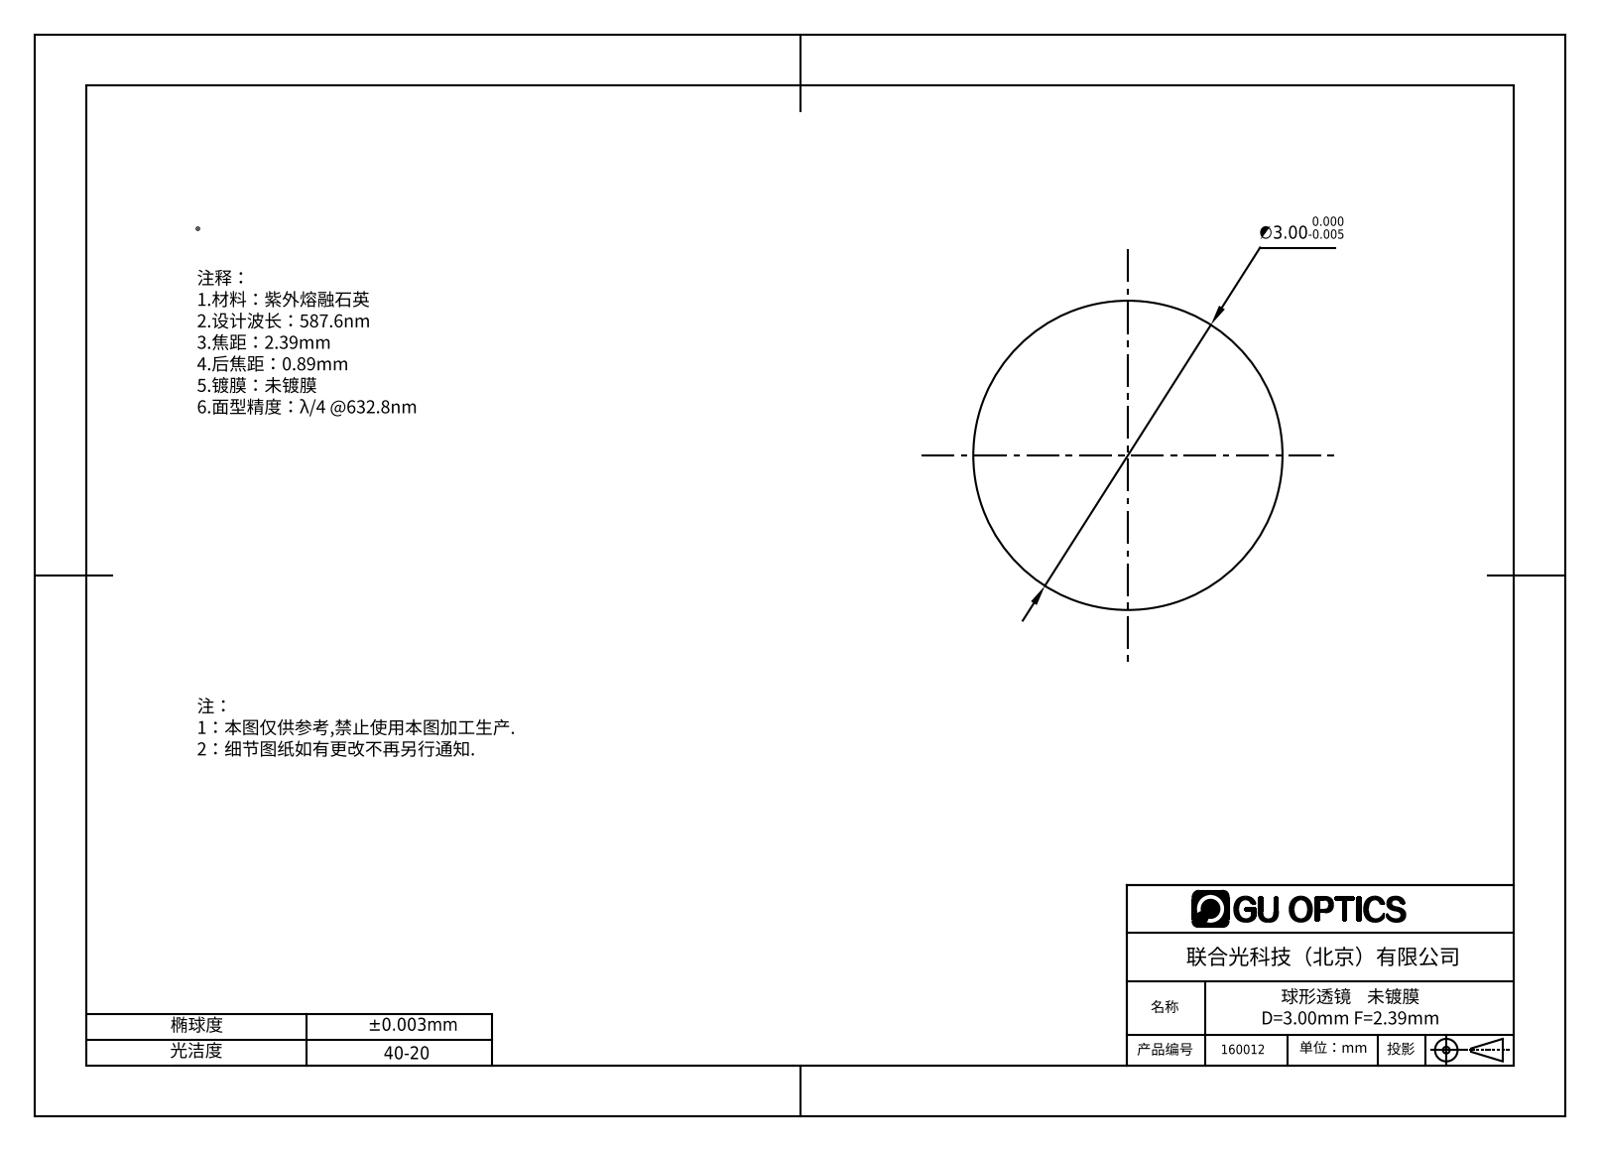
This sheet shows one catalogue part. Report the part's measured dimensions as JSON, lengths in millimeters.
{"part_name": "160002", "step_written_by": "SolidWorks 2016 (CONFIG_CONTROL_DESIGN)", "units": "millimeters", "bodies": {"solids": 1, "faces": 2, "planar": 0, "cylindrical": 0, "other": 2}, "overall_size": [3, 3, 3], "volume_mm3": 14, "surface_area_mm2": 28}
